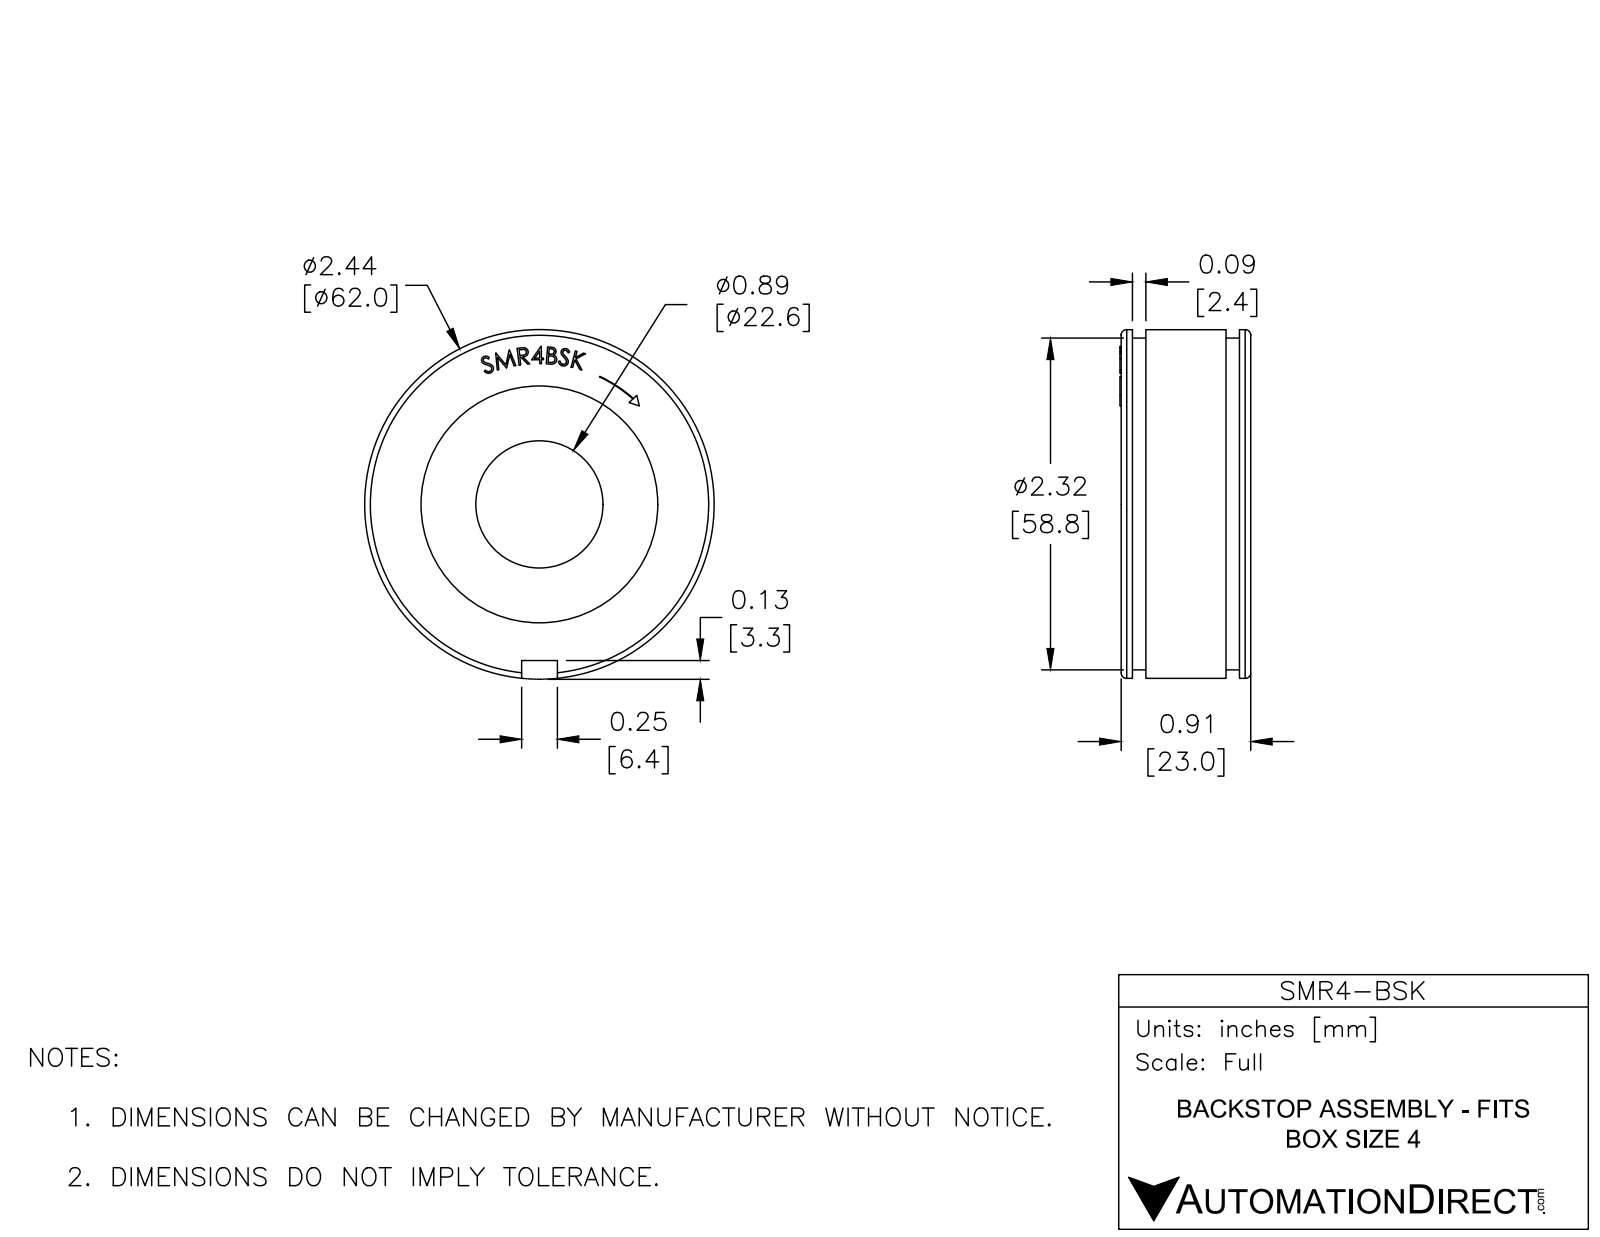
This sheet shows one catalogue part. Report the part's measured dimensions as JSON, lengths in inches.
{"part_name": "SMR4-BSK", "step_written_by": "SolidWorks 2016 (AUTOMOTIVE_DESIGN)", "units": "inches", "bodies": {"solids": 1, "faces": 162, "planar": 89, "cylindrical": 23, "other": 50}, "overall_size": [2.441, 2.435, 0.913], "volume_in3": 3.501, "surface_area_in2": 19.25, "round_holes": [[0.889, 1], [1.654, 1]], "round_bosses_or_shafts": [[2.441, 1], [2.323, 1]], "partial_cylinders_radius": [[0.984, 1], [0.988, 1]], "face_to_face_distances": [0.02, 0.886, 0.906, 0.866, 0.079, 0.827, 0.059, 0.807, 0.173, 0.732]}
